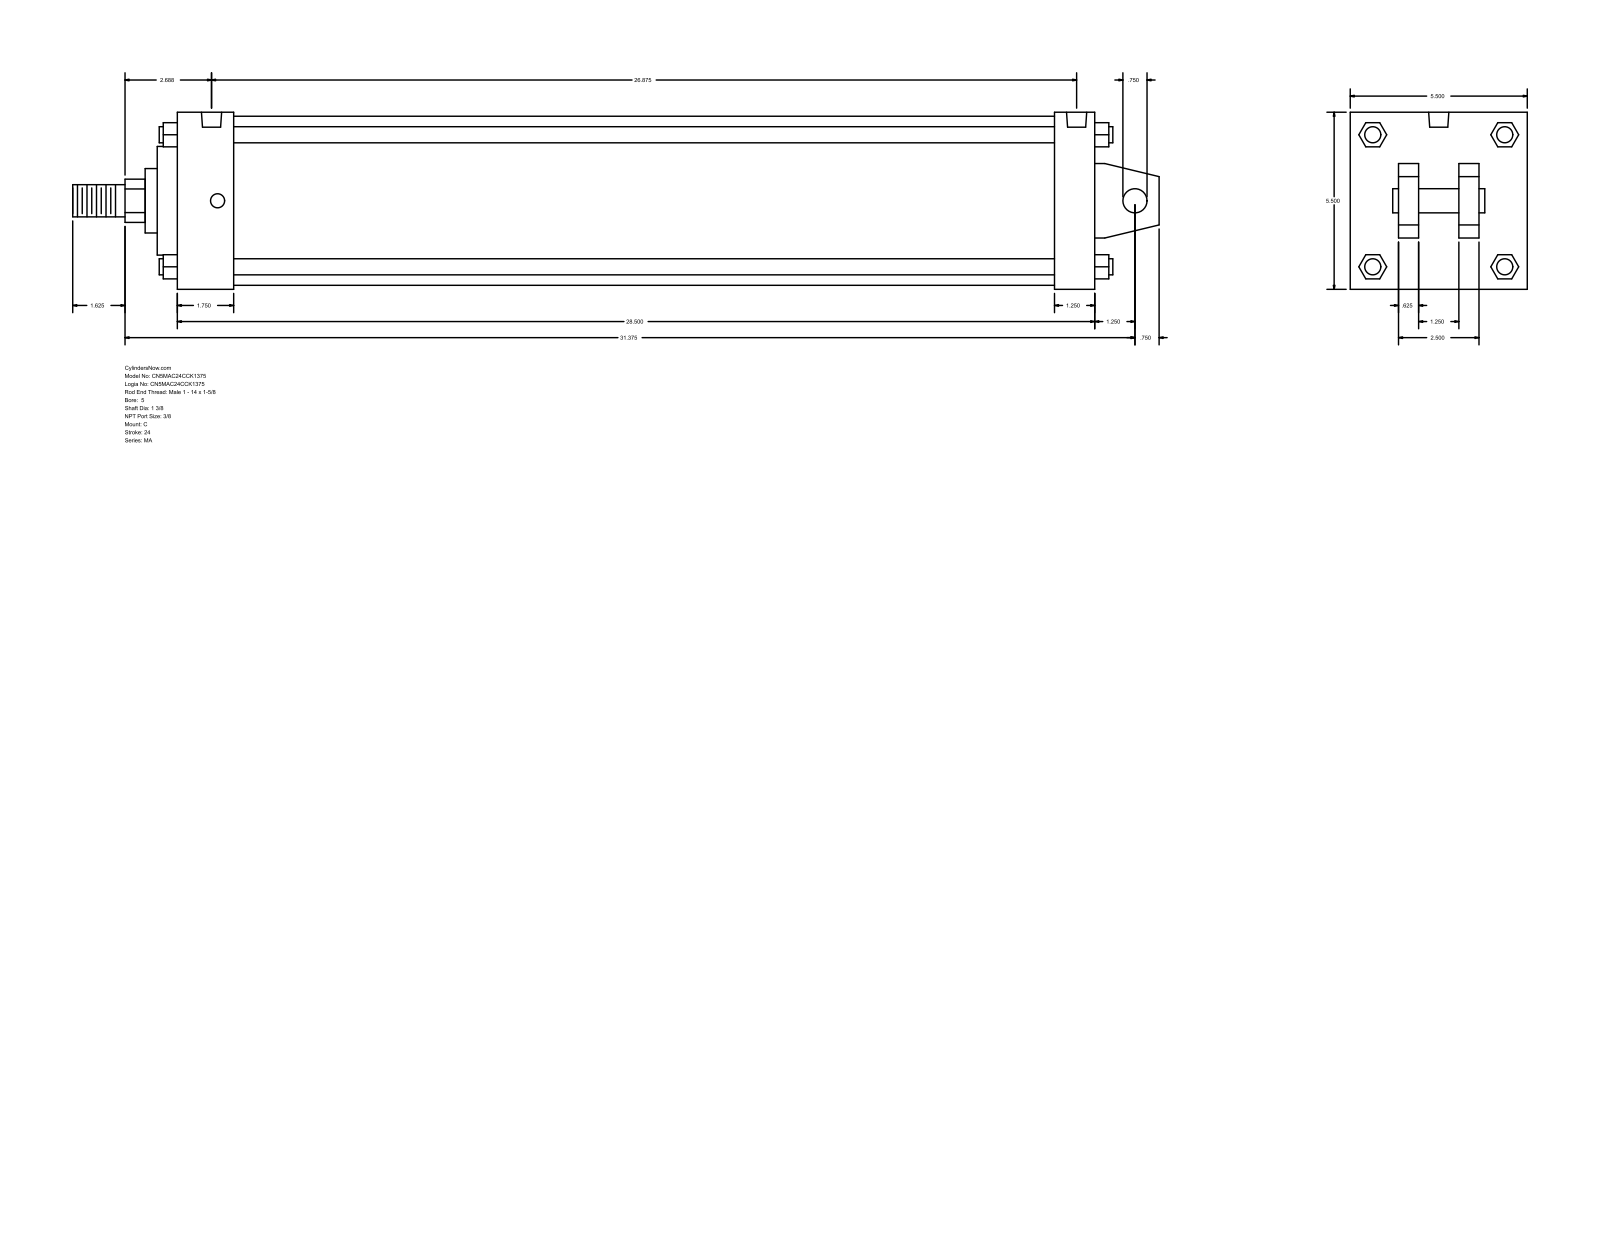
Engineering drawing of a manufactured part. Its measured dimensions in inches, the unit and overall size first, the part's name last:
Units: inches
Overall size (bounding box): 33.75 × 5.5 × 5.5
Round holes (diameter × count): ⌀0.437 ×4, ⌀0.627 ×2
Round bosses / shafts (diameter × count): ⌀0.5 ×4, ⌀5.25 ×1, ⌀3.375 ×1, ⌀2 ×1, ⌀1.375 ×1, ⌀1 ×1, ⌀0.75 ×1
Partial cylindrical surfaces — rounded edges, fillets, slot ends (radius × count): R0.672 ×1
Main face-to-face distances: 5.5, 28.5, 0.625, 27.25, 1.25, 1.75, 25.5, 26.75, 2.125, 1.5
Hole centre spacings: 0.188, 26.5, 26.687, 26.875
Bodies: 0 solids, 141 faces (109 planar, 32 cylindrical, 0 other)
Part name (STEP PRODUCT): MA_C__0500_1.375
STEP written by: GSSL Pune (CONFIG_CONTROL_DESIGN)
